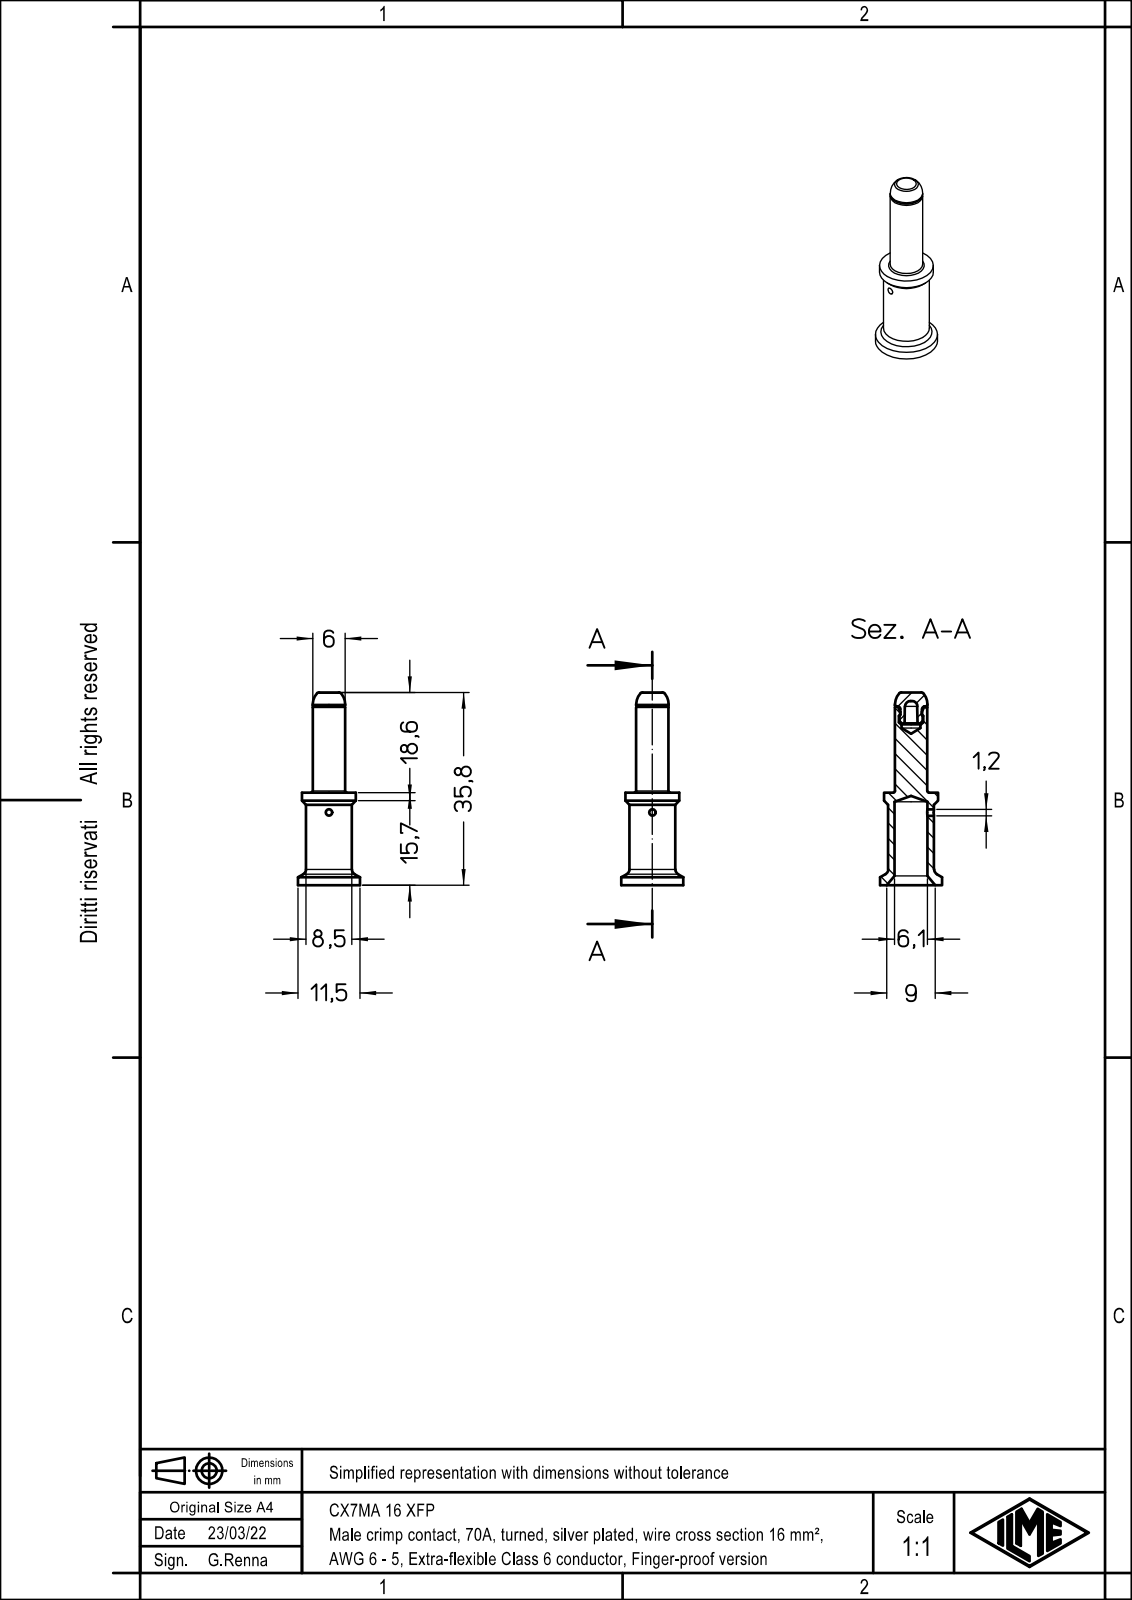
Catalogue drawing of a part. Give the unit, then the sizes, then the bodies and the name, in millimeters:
Units: millimetres
Overall size (bounding box): 35.8 × 11.5 × 11.5
Round holes (diameter × count): ⌀1.2 ×1, ⌀3.5 ×1, ⌀4.5 ×1, ⌀6.1 ×1
Round bosses / shafts (diameter × count): ⌀11.5 ×1, ⌀10 ×1, ⌀8.5 ×1, ⌀6 ×1, ⌀4.3 ×1, ⌀4 ×1
Main face-to-face distances: 17.2, 35.8, 18.6, 30, 12.8, 5.8, 34.2, 17, 4.2, 1.6
Volume: 1 096 mm³ · Surface area: 1 466 mm²
Bodies: 1 solid, 69 faces (5 planar, 24 cylindrical, 40 other)
Part name (STEP PRODUCT): 54702.16XF_B; CX7MA_16_XFP
STEP written by: Creo Elements/Direct Modeling 20.1B 02-Apr-2019 (C) Parametric Technology GmbH (AUTOMOTIVE_DESIGN)
